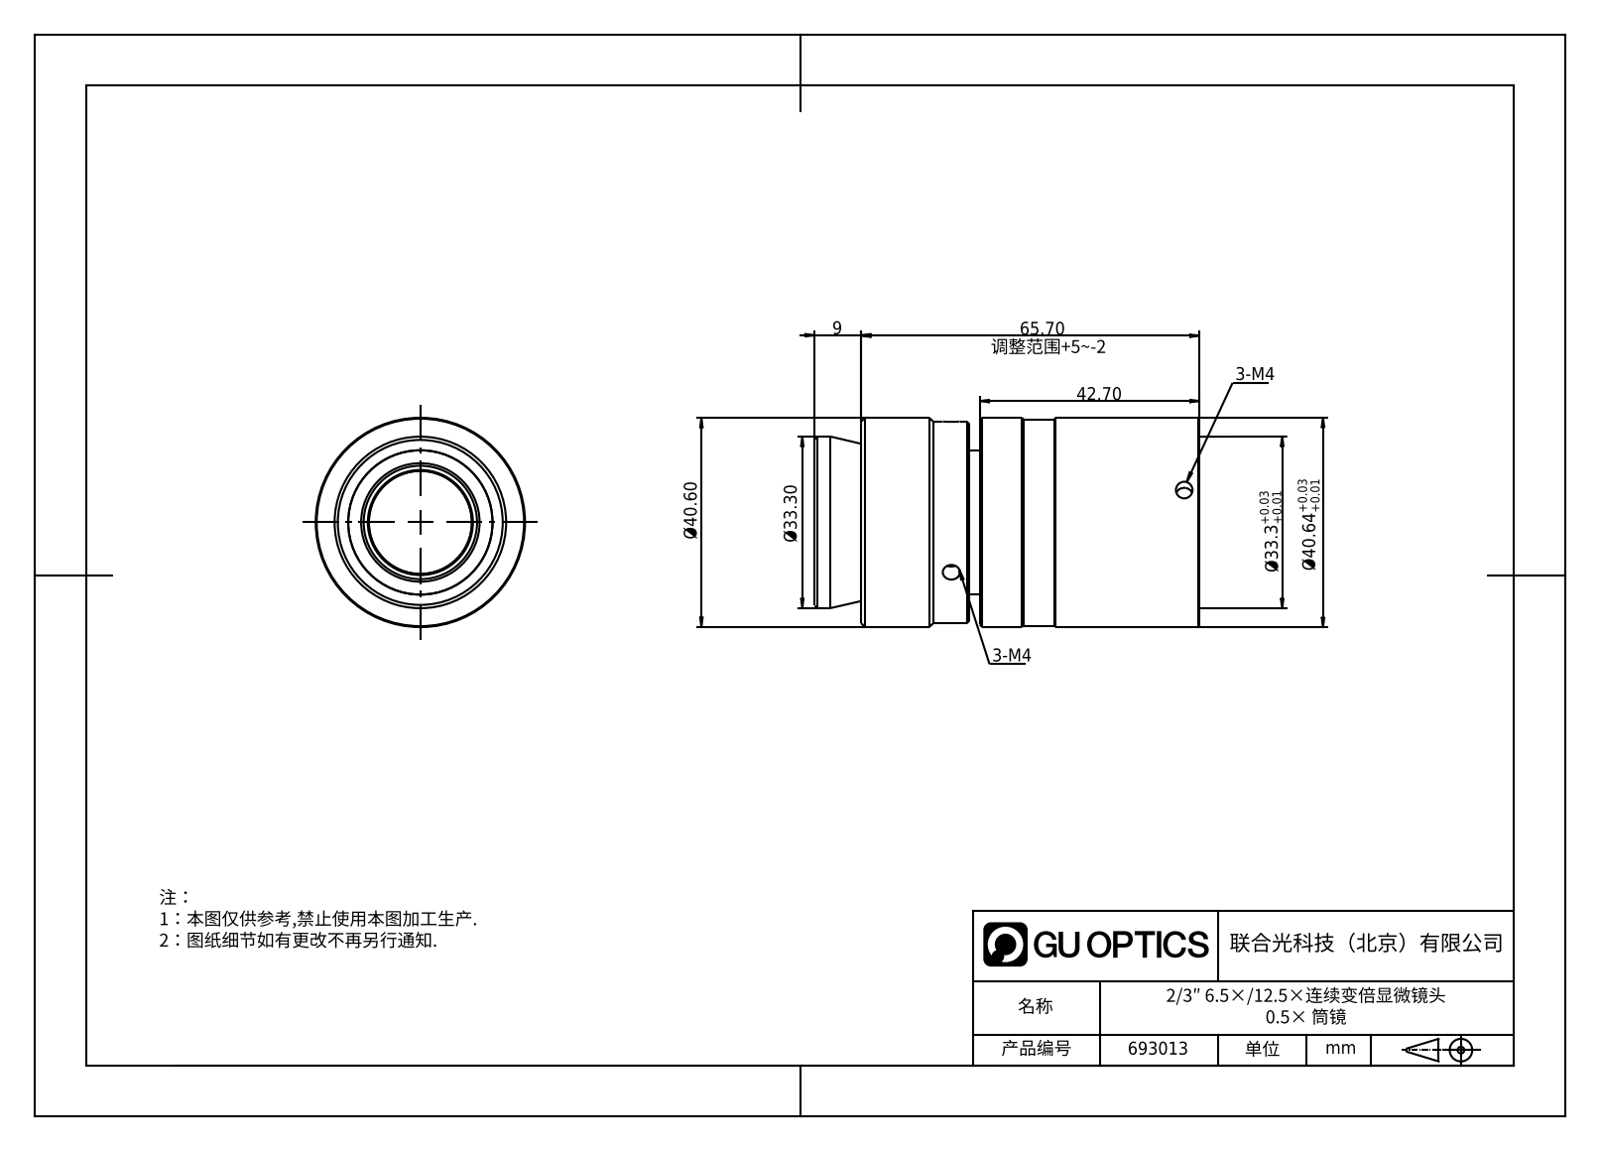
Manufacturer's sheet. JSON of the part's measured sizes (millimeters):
{"part_name": "693013", "step_written_by": "SolidWorks 2020 (CONFIG_CONTROL_DESIGN)", "units": "millimeters", "bodies": {"solids": 0, "faces": 35, "planar": 6, "cylindrical": 15, "other": 14}, "overall_size": [74.7, 40.64, 40.64], "round_holes": [[3.3, 6], [23, 1], [32, 1]], "round_bosses_or_shafts": [[40.64, 1], [40.6, 1], [40.04, 1], [39.14, 1], [33.3, 1], [28, 1]], "face_to_face_distances": [2, 23, 21, 32, 30, 9, 42.69, 44.69, 65.69, 74.69]}
